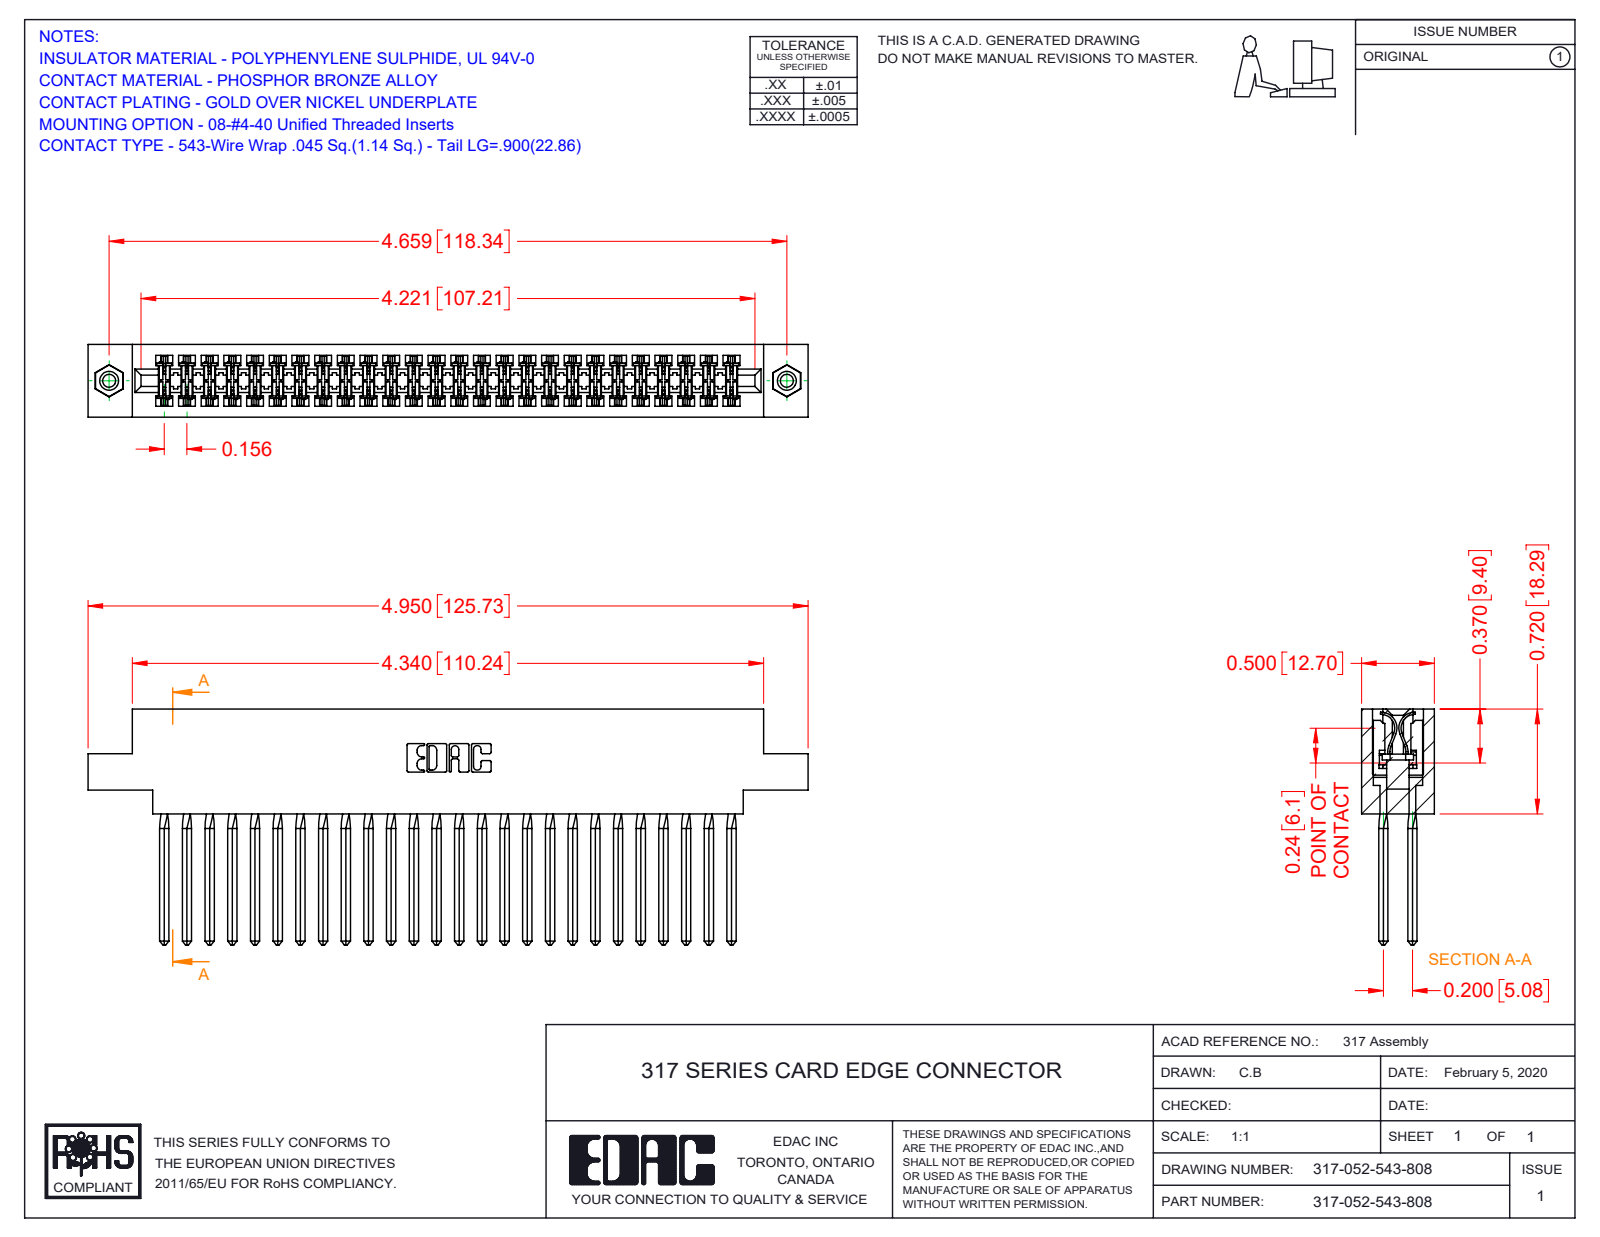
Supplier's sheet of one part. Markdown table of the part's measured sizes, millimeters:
| quantity | value |
| --- | --- |
| part name | 317-052-543-878; 317-290-001_543; 345-250-001_345-250-003-102; 317 Part_.156 Dia - TI |
| STEP written by | SolidWorks 2016 (CONFIG_CONTROL_DESIGN) |
| units | millimeters |
| bodies | 55 solids, 4790 faces (3886 planar, 680 cylindrical, 224 other) |
| overall size | 125.7 × 41.1 × 12.7 |
| volume | 20 810 mm³ |
| surface area | 30 970 mm² |
| round holes (diameter × count) | 2.3 × 2, 3.2 × 2, 4 × 2 |
| round bosses / shafts (diameter × count) | 3.9 × 2 |
| partial cylindrical surfaces (radius × count) | 0.4 × 104, 0.3 × 22, 0.2 × 6, 0.8 × 6, 0.7 × 3, 2.4 × 2, 2.5 × 2, 2.8 × 2 |
| main face-to-face distances | 12.7, 1.9, 10.8, 2.8, 8.9, 5, 2.4, 5.1, 18.3, 2.9 |
| hole center spacings | 118.3 |
